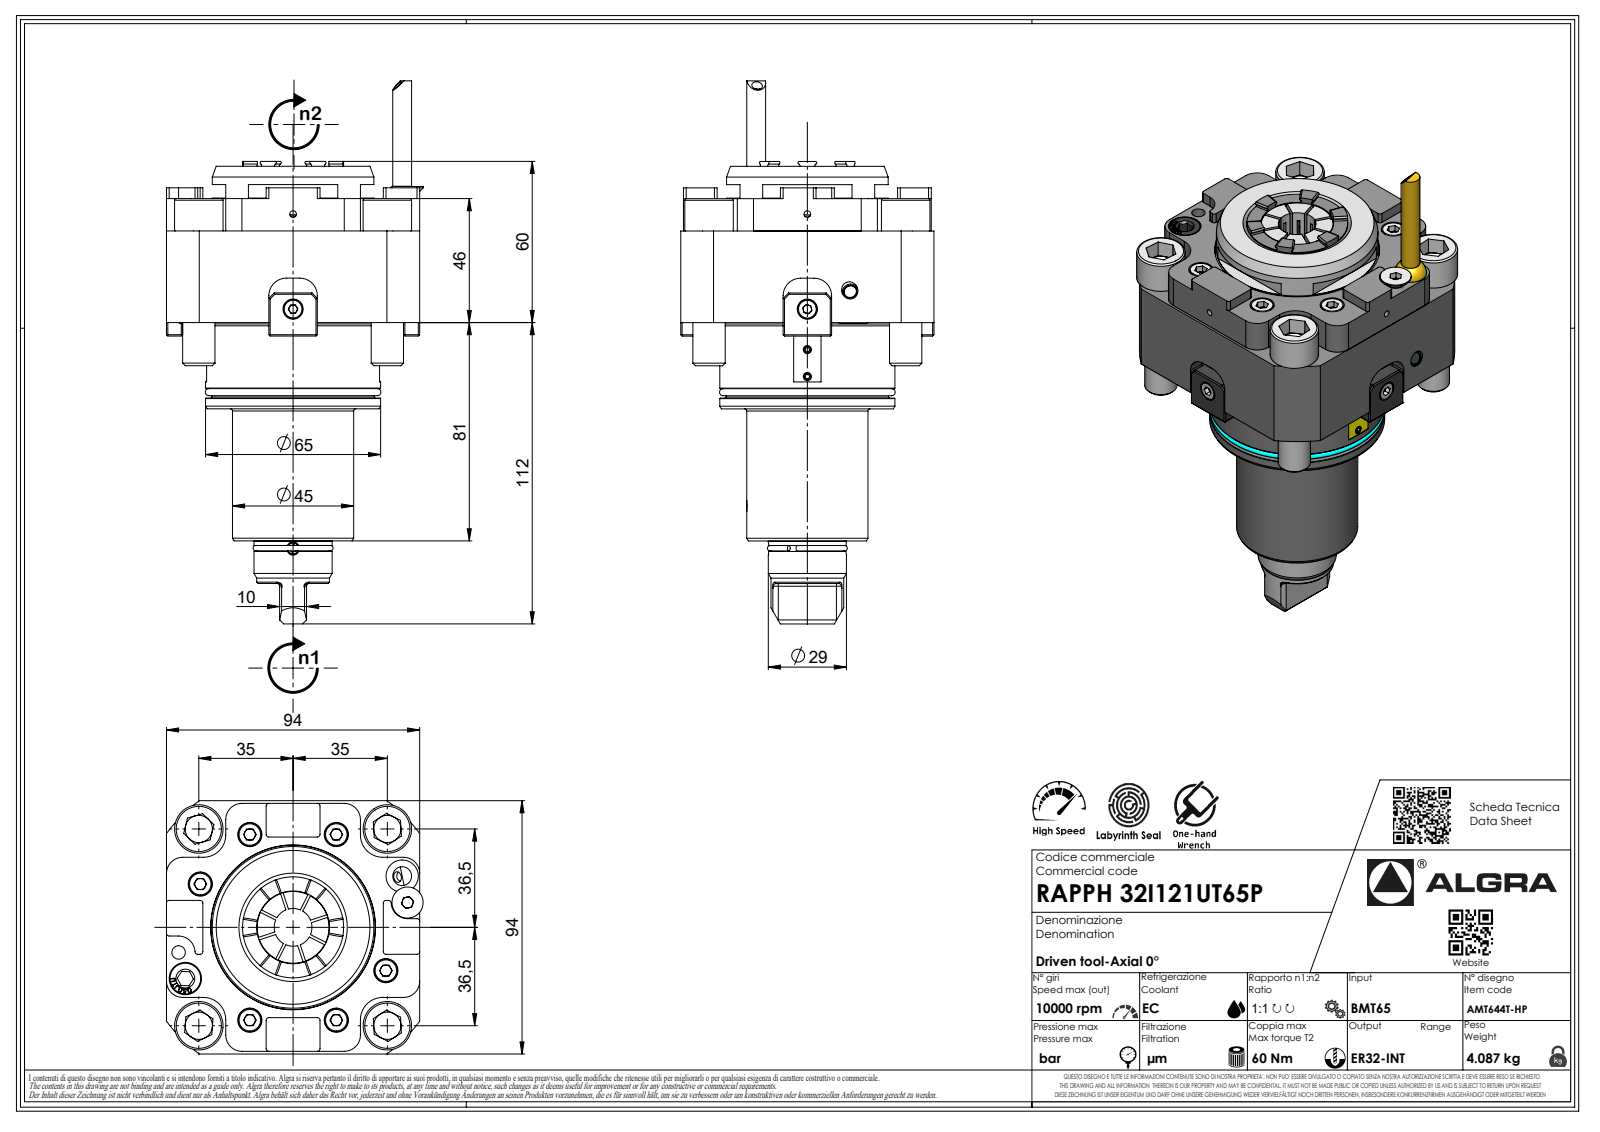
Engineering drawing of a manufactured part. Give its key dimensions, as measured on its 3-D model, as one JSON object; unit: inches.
{"part_name": "RAPPH32I121UT65P", "step_written_by": "SolidWorks 2023 (AUTOMOTIVE_DESIGN)", "units": "inches", "bodies": {"solids": 1, "faces": 653, "planar": 420, "cylindrical": 104, "other": 129}, "overall_size": [6.756, 3.701, 3.701], "volume_in3": 38.1, "surface_area_in2": 94.59, "round_holes": [[0.083, 1], [1.063, 1]], "round_bosses_or_shafts": [[0.709, 4], [0.472, 4], [2.559, 1], [2.374, 1], [2.362, 1], [1.772, 1], [1.142, 1], [0.251, 1]], "partial_cylinders_radius": [[0.039, 24], [0.236, 8], [0.013, 7], [0.02, 7], [0.146, 7], [0.256, 4], [0.325, 4], [0.24, 2]], "face_to_face_distances": [3.701, 1.811, 0.472, 0.63, 2.283, 1.969, 3.071, 1.26, 2.598, 0.039]}
